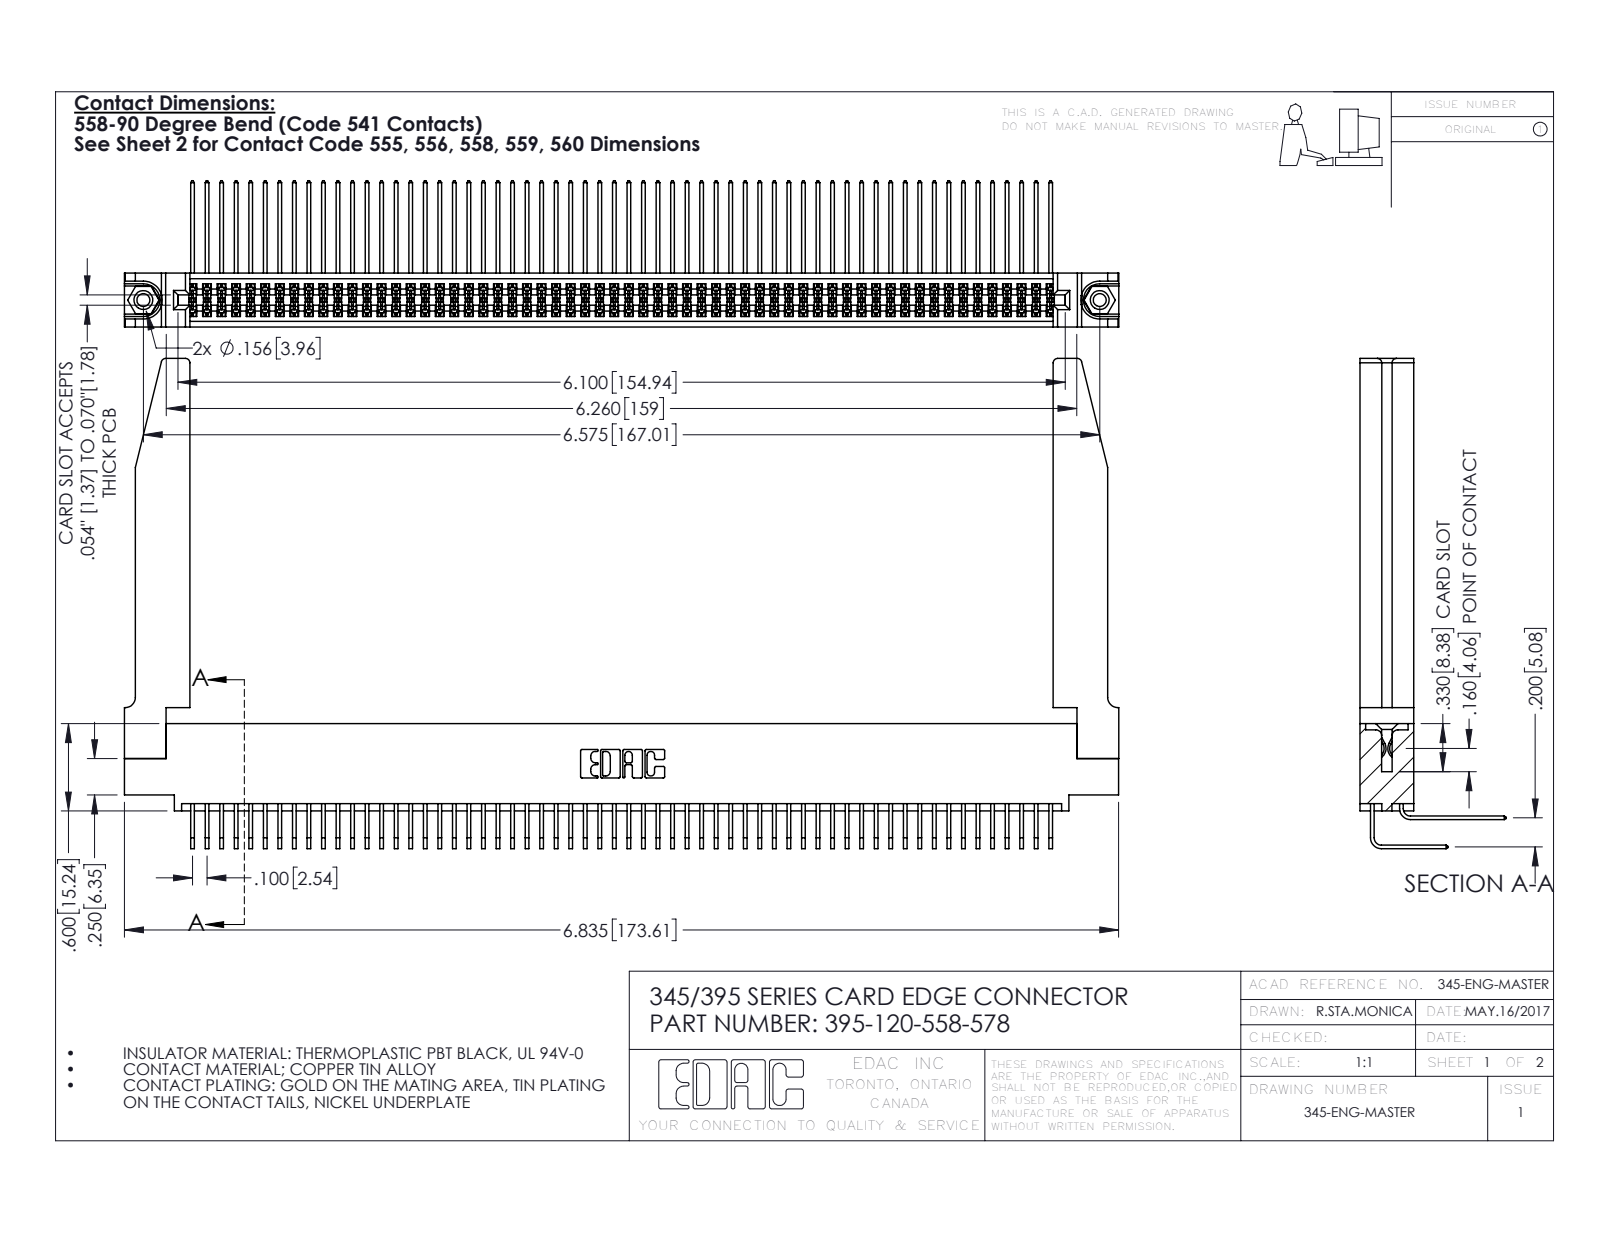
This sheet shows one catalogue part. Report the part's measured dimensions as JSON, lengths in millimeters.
{"part_name": "395-120-558-578; 345-220-078_345-220-078; 345 Part_0.110 Offset - 0.156 Dia-TH; 345-292-001_558 Tail - 2 (+2 more)", "step_written_by": "SolidWorks 2016 (CONFIG_CONTROL_DESIGN)", "units": "millimeters", "bodies": {"solids": 125, "faces": 6604, "planar": 4426, "cylindrical": 2126, "other": 52}, "overall_size": [173.6, 85.6, 25.5], "volume_mm3": 25420, "surface_area_mm2": 36630, "round_holes": [[2.3, 2], [3.2, 2], [4, 2], [1.6, 1]], "round_bosses_or_shafts": [[3.9, 2]], "partial_cylinders_radius": [[0.2, 181], [0.3, 22], [0.8, 8], [0.2, 6], [0.8, 6], [0.7, 3], [0.4, 2], [0.5, 2]], "face_to_face_distances": [1.8, 7.6, 9.4, 5.1, 2.5, 6.9, 0.6, 5.7, 0.6, 4.4], "hole_center_spacings": [6.9, 161, 167]}
